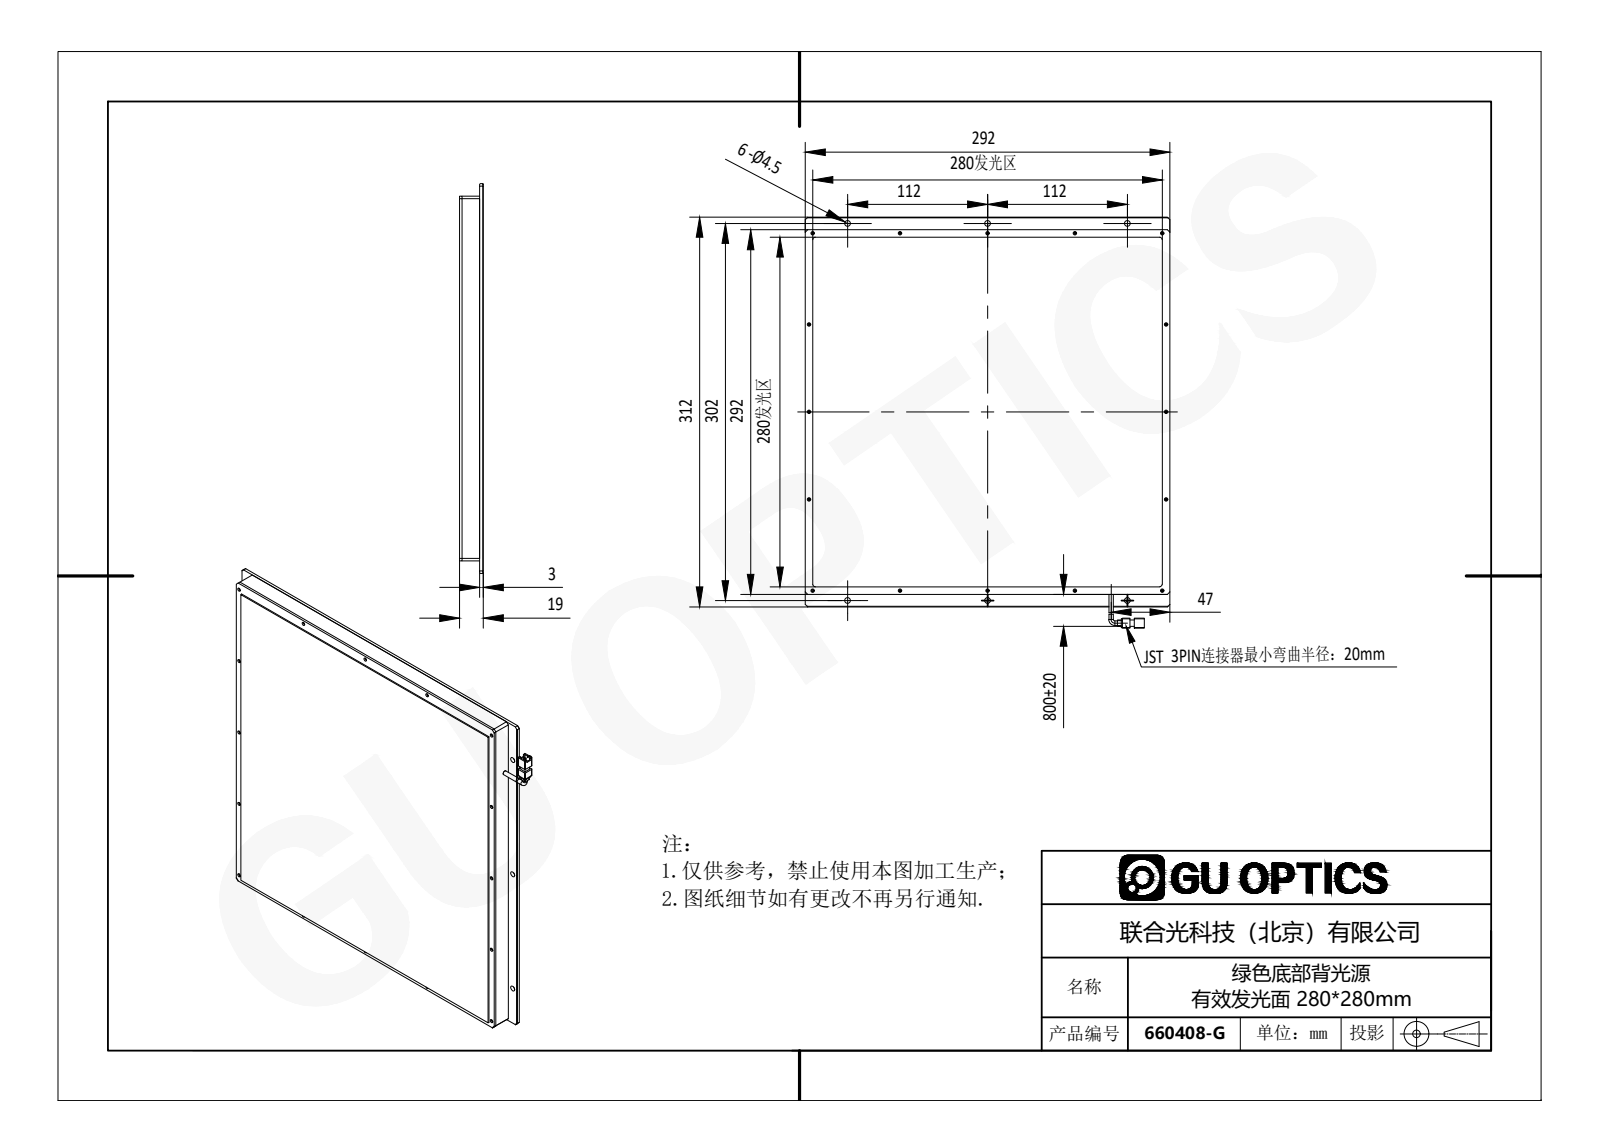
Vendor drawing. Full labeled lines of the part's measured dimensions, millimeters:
Part name (STEP PRODUCT): 660408-G
STEP written by: SolidWorks 2016 (AUTOMOTIVE_DESIGN)
Units: millimetres
Bodies: 5 solids, 539 faces (169 planar, 270 cylindrical, 100 other)
Overall size (bounding box): 329 × 292 × 20
Volume: 614 608 mm³ · Surface area: 407 504 mm²
Round holes (diameter × count): ⌀1.6 ×32, ⌀1.25 ×16, ⌀1.5 ×16, ⌀2 ×16, ⌀2.4 ×16, ⌀2.8 ×16, ⌀4.5 ×6
Round bosses / shafts (diameter × count): ⌀3.5 ×2
Partial cylindrical surfaces — rounded edges, fillets, slot ends (radius × count): R0.5 ×8, R1 ×8, R2 ×6
Main face-to-face distances: 17, 3, 14, 20, 6, 286, 292, 16, 1, 280
Hole centre spacings: 286, 70, 294.44, 80, 210, 296.98, 140, 160.56
